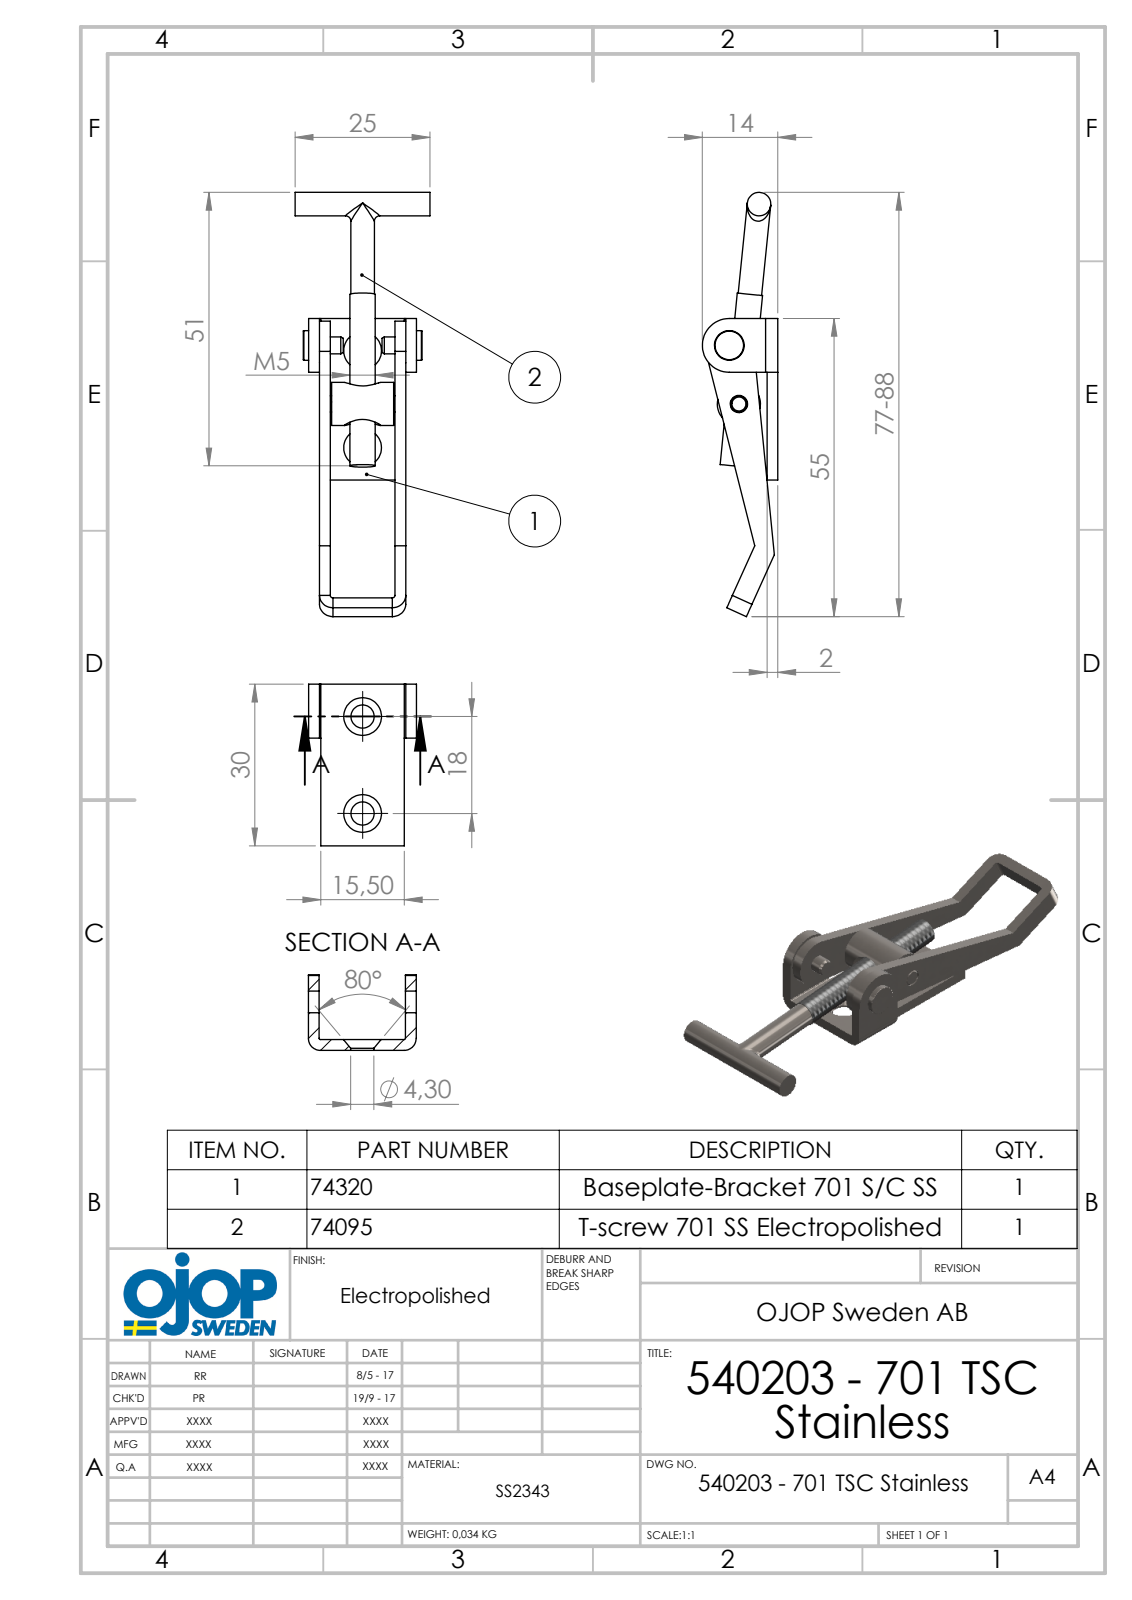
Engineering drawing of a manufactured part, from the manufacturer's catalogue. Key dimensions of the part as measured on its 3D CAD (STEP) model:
Part name (STEP PRODUCT): 701 - Bygel; 701 - SC; 701 - Ansatsnit; 540203 (+2 more)
STEP written by: SolidWorks 2015 (AUTOMOTIVE_DESIGN)
Units: millimetres
Bodies: 6 solids, 129 faces (51 planar, 56 cylindrical, 22 other)
Overall size (bounding box): 78.83 × 25 × 14
Volume: 4 380 mm³ · Surface area: 5 363 mm²
Round holes (diameter × count): ⌀4.3 ×3, ⌀3.2 ×2, ⌀4.5 ×1
Round bosses / shafts (diameter × count): ⌀4.36 ×2, ⌀8 ×1, ⌀5.5 ×1, ⌀4.7 ×1, ⌀3.15 ×1, ⌀3 ×1
Partial cylindrical surfaces — rounded edges, fillets, slot ends (radius × count): R0.5 ×4, R2.5 ×4, R4.5 ×1, R5 ×1
Main face-to-face distances: 2, 14, 2.25, 16, 16.25, 12, 4.25, 18.25, 18.5, 14.25
Hole centre spacings: 11.02, 18
